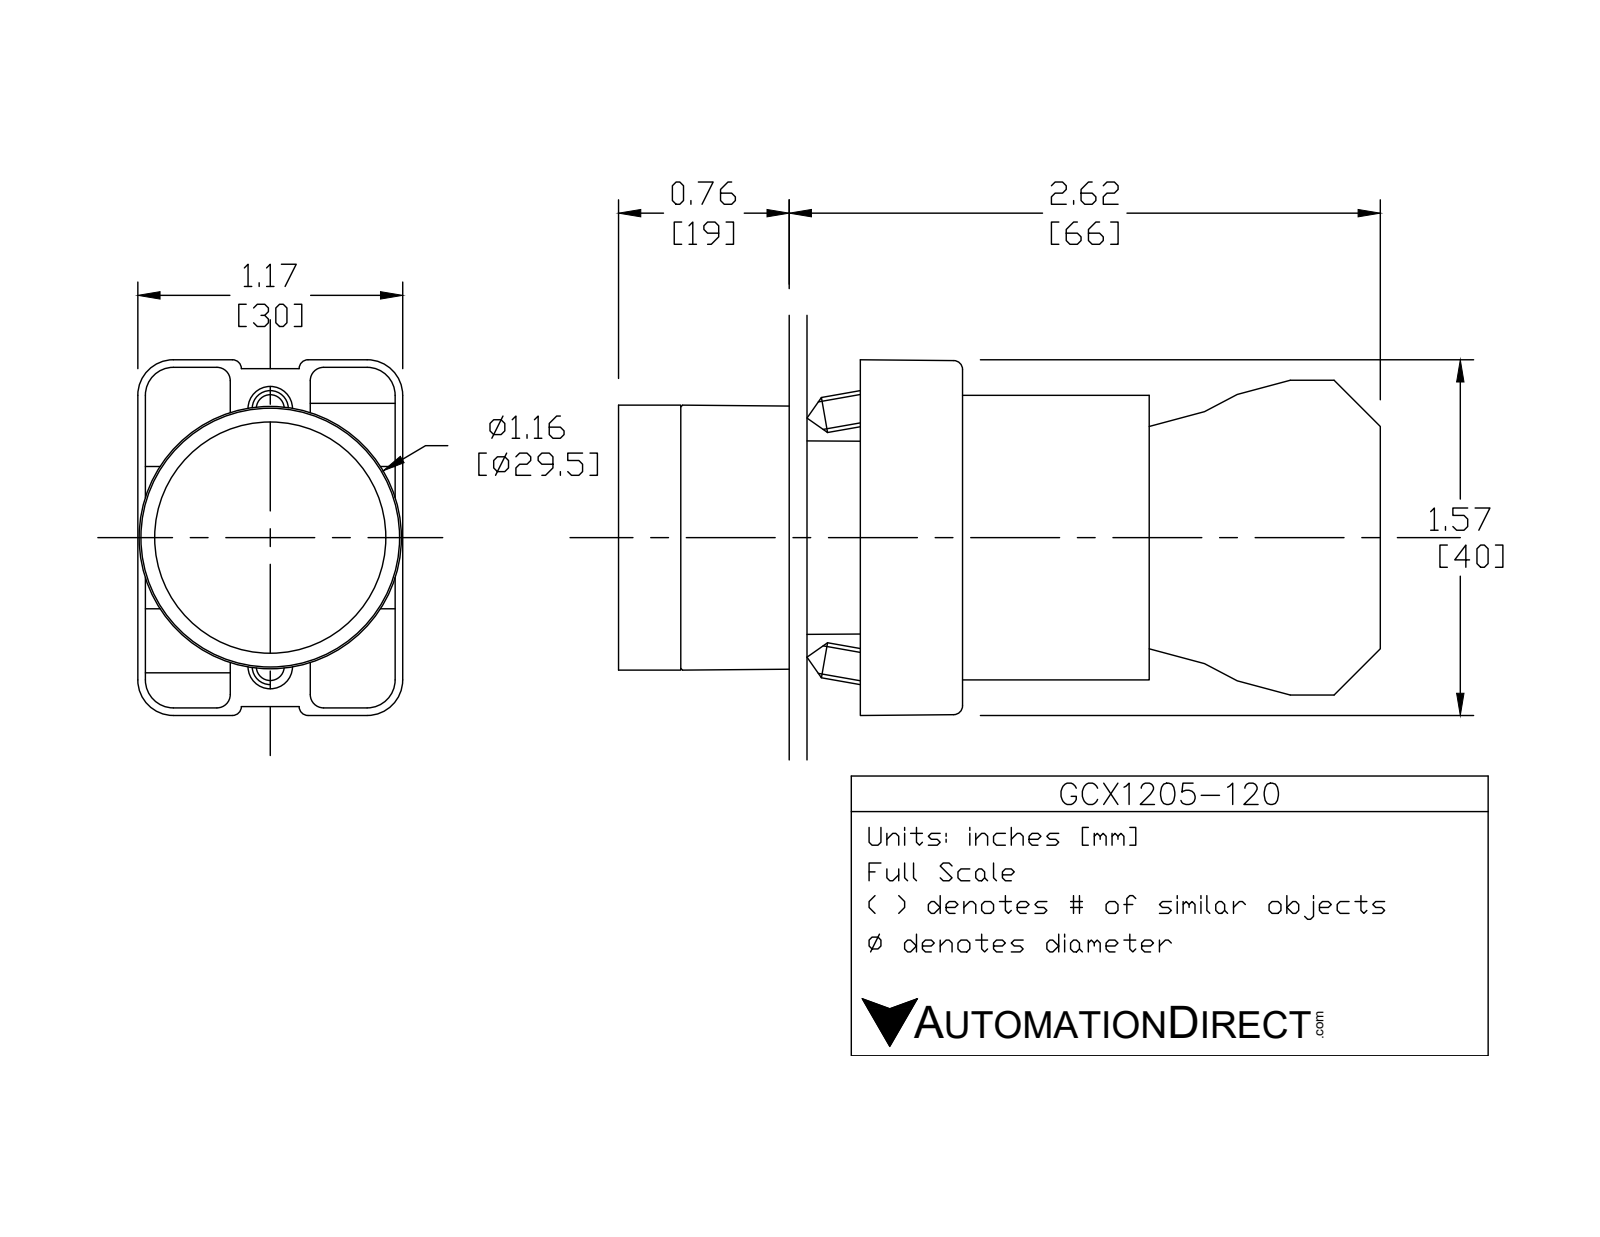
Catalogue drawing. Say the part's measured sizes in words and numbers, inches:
The part is named "GCX1205-120; ECX1050; GCX1205 OPERATOR; ecx1040 (+1 more)". Its 3-D file was written by "SolidWorks 2016 (AUTOMOTIVE_DESIGN)". It is 8 solids with 431 faces: 252 planar, 148 cylindrical and 31 other. Overall it measures 3.319 by 1.581 by 1.177 inches. Its volume is 2.794 cubic inches and its surface area 38.75 square inches. Round holes: 2 of diameter 0.079, 2 of diameter 0.124, 2 of diameter 0.13, 1 of diameter 0.087, 1 of diameter 0.197, 1 of diameter 0.469, 1 of diameter 0.878, 1 of diameter 0.888, 1 of diameter 1.024. Round bosses or shafts: 4 of diameter 0.157, 1 of diameter 1.175, 1 of diameter 1.004, 1 of diameter 0.945, 1 of diameter 0.856, 1 of diameter 0.78, 1 of diameter 0.504. Partial cylindrical surfaces (rounded edges, fillets, slot ends): 24 of radius 0.059, 12 of radius 0.041, 12 of radius 0.124, 12 of radius 0.157, 8 of radius 0.039, 2 of radius 0.128, 1 of radius 0.02, 1 of radius 0.063. The main face-to-face distances are 0.827, 2.02, 1.193, 0.579, 1.171, 0.031, 0.276, 0.033, 0.748, 0.573. The hole center spacings are 0.236, 0.544, 0.472, 0.49.
